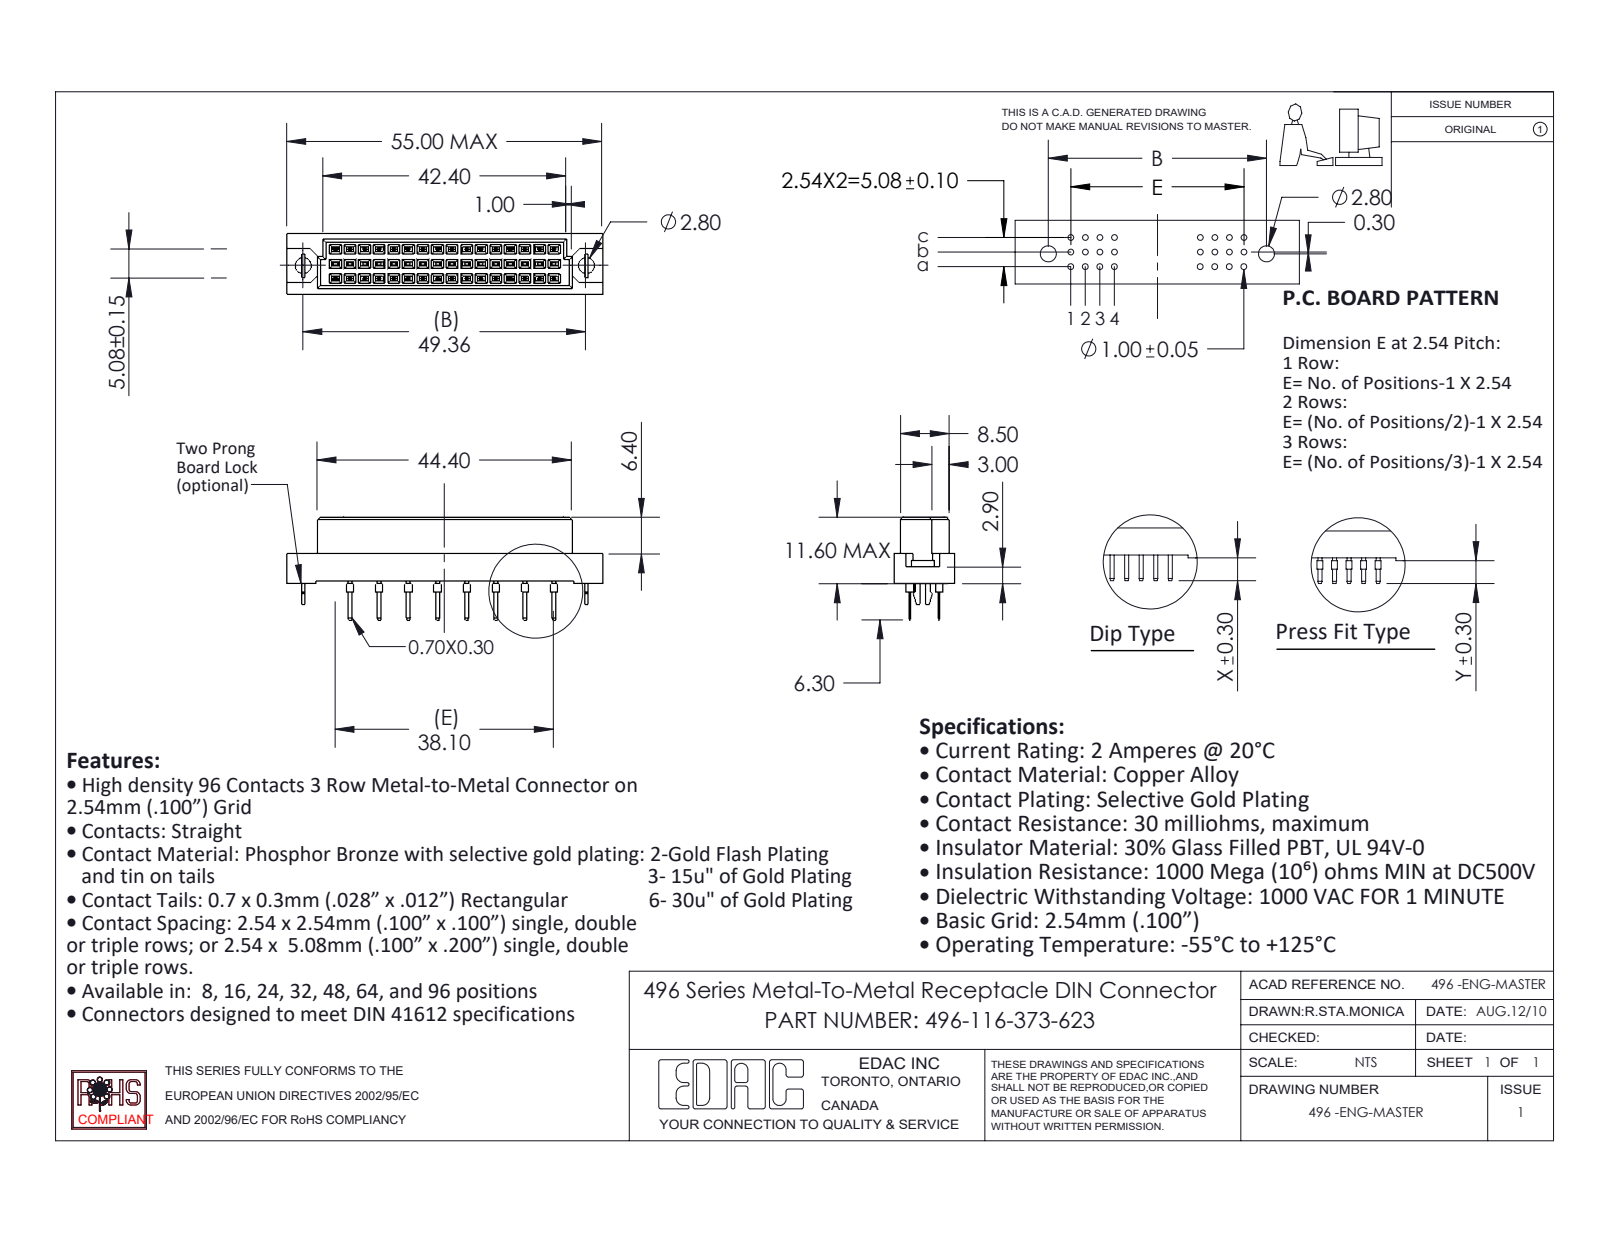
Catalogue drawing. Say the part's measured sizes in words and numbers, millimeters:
The part is named "496-290_73; 496 Bore-lock; 496 Part_48; 496-116-373-623". Its 3-D file was written by "SolidWorks 2020 (CONFIG_CONTROL_DESIGN)". It is 19 solids with 990 faces: 952 planar, 38 cylindrical and 0 other. Overall it measures 55 by 17.9 by 10.6 millimeters. Its volume is 4 662 cubic millimeters and its surface area 4 721 square millimeters. Round holes: 2 of diameter 2.8. Round bosses or shafts: 16 of diameter 1. Partial cylindrical surfaces (rounded edges, fillets, slot ends): 1 of radius 0.53. The main face-to-face distances are 2.54, 5.08, 1.05, 9.55, 0.81, 0.56, 10.6, 0.55, 3.35, 1.73. The hole center spacings are 49.36.
